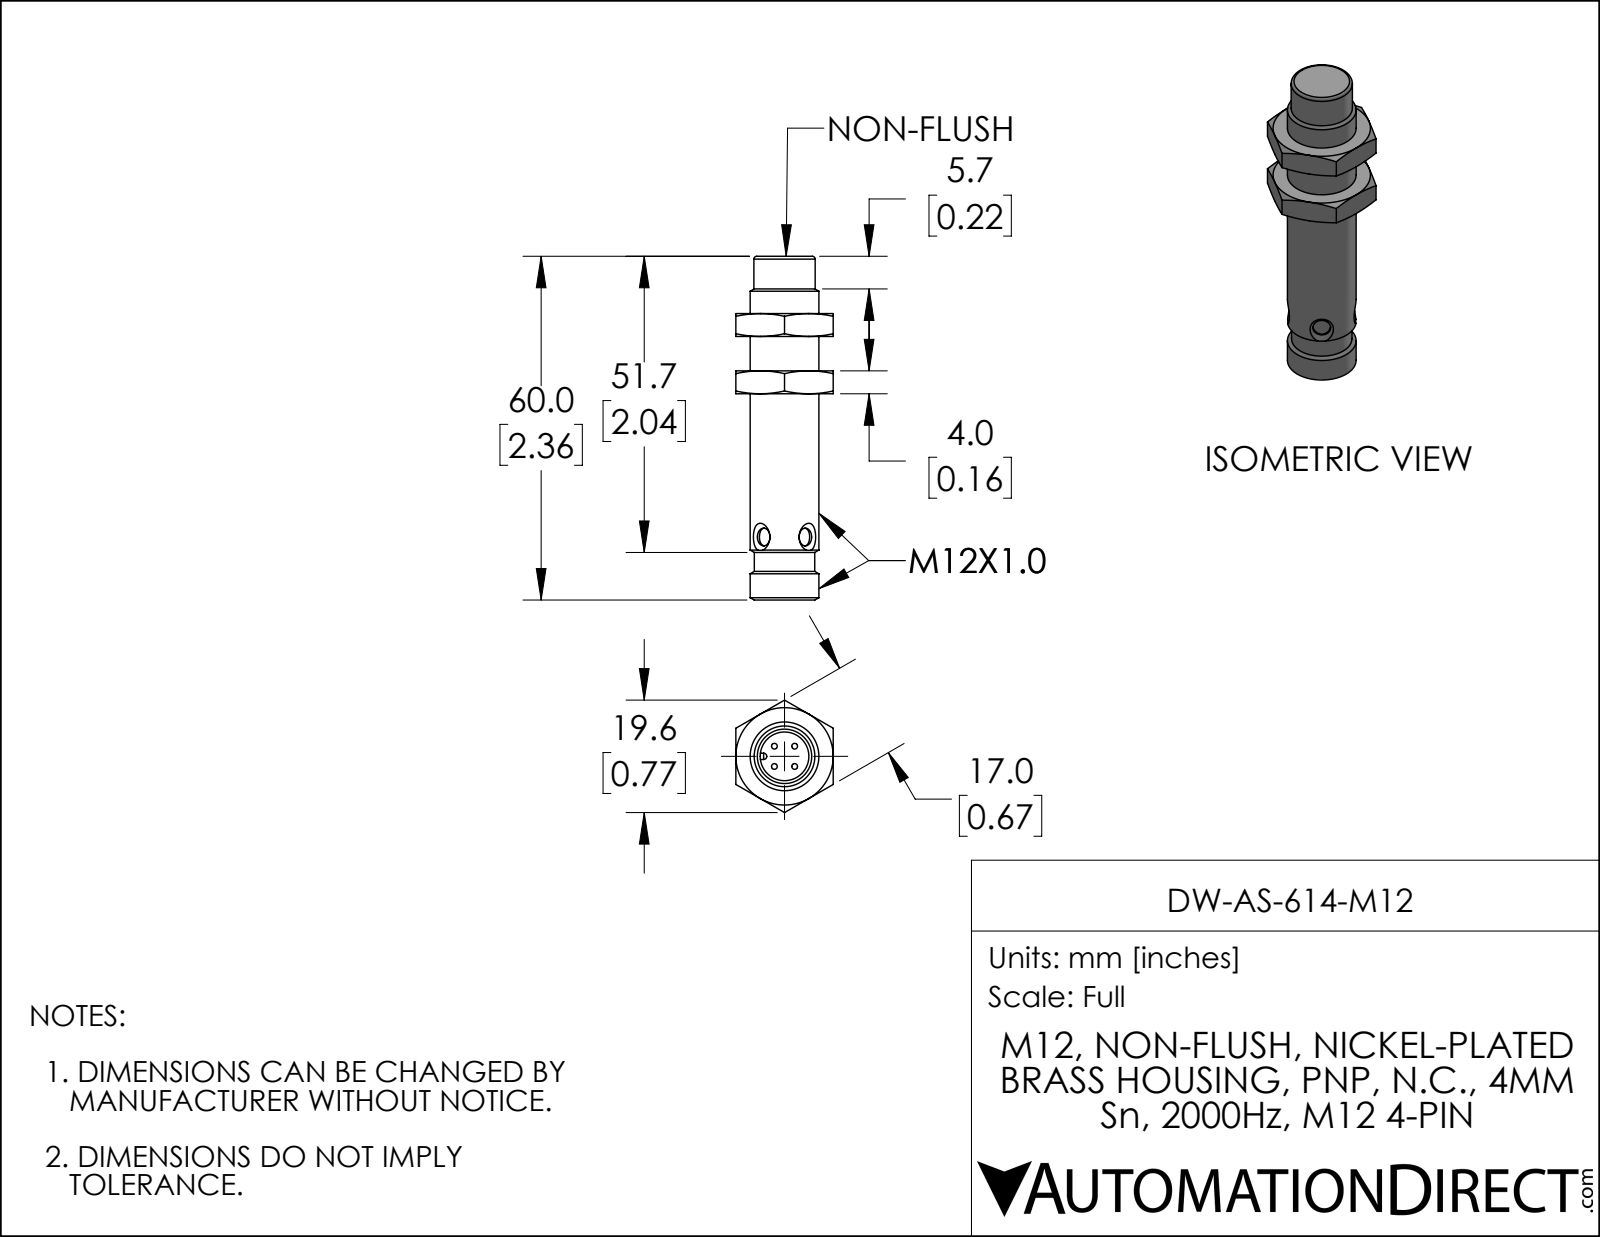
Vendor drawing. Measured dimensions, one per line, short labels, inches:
name: DW-AS-614-M12
written by: SolidWorks 2019 (AUTOMOTIVE_DESIGN)
unit: in
bodies: 1 solid, 82 faces (22 planar, 21 cylindrical, 39 other)
size: 2.362 × 0.773 × 0.669
volume: 0.435 in³; area: 5.403 in²
holes: 2× ⌀0.122, 1× ⌀0.335
bosses: 4× ⌀0.039, 1× ⌀0.472, 1× ⌀0.421, 1× ⌀0.415
rounds: 2× R0.022, 1× R0.193
face distances: 0.394, 0.157, 0.669, 0.551, 0.236, 0.787, 0.945, 2.022, 1.629, 1.471
